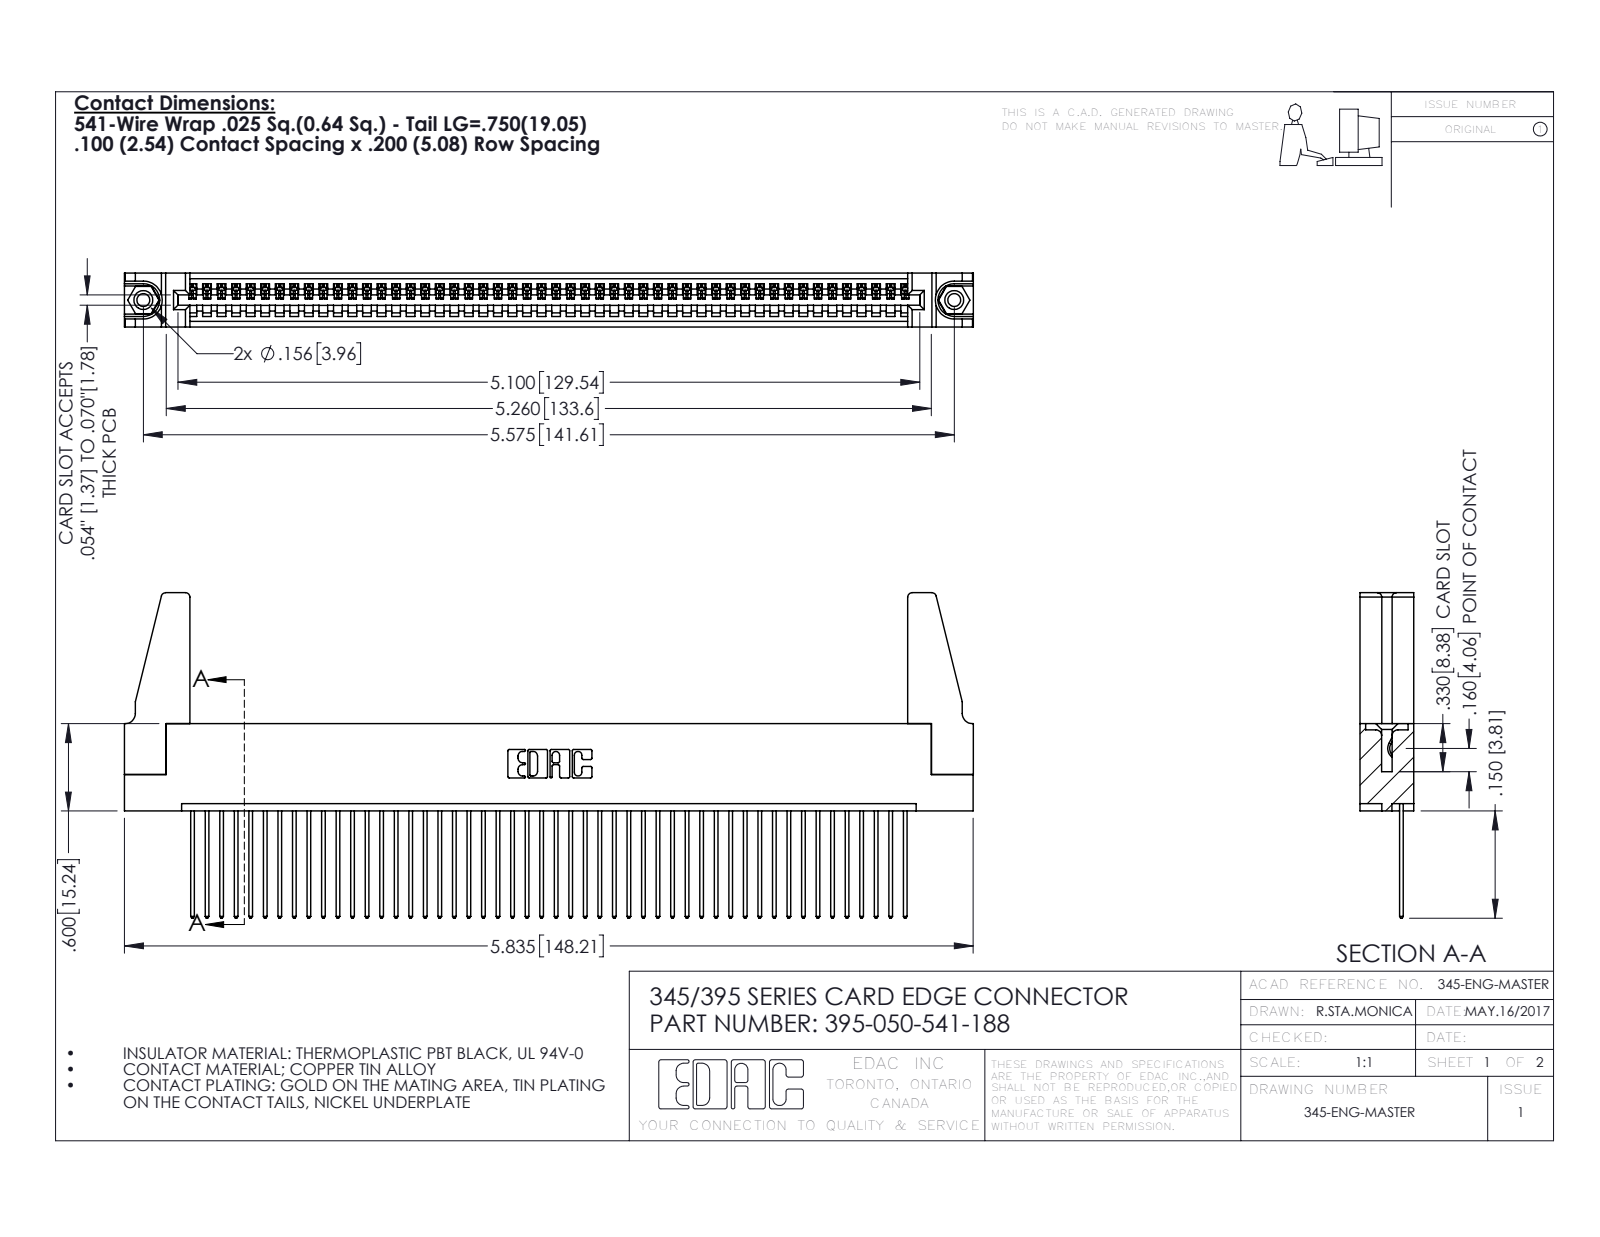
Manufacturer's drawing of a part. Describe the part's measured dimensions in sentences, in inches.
The part is named "345 Part_Flush Mounting Lugs - 0.156 Dia-TH; 345-250-001_345-250-001-102; 345-220-078_345-220-088; 345-292-001_345-293-141 (+1 more)". Its 3-D file was written by "SolidWorks 2016 (CONFIG_CONTROL_DESIGN)". It is 55 solids with 3150 faces: 2152 planar, 982 cylindrical and 16 other. Overall it measures 5.836 by 2.237 by 0.37 inches. Its volume is 1.072 cubic inches and its surface area 36 square inches. Round holes: 2 of diameter 0.089, 2 of diameter 0.125, 2 of diameter 0.156, 1 of diameter 0.064. Round bosses or shafts: 2 of diameter 0.155. Partial cylindrical surfaces (rounded edges, fillets, slot ends): 100 of radius 0.006, 100 of radius 0.01, 22 of radius 0.01, 8 of radius 0.03, 6 of radius 0.007, 6 of radius 0.031, 3 of radius 0.026, 2 of radius 0.031. The main face-to-face distances are 0.072, 0.298, 0.37, 0.098, 0.272, 0.025, 0.2, 0.225, 0.149, 0.072. The hole center spacings are 0.27, 5.339, 5.575.
